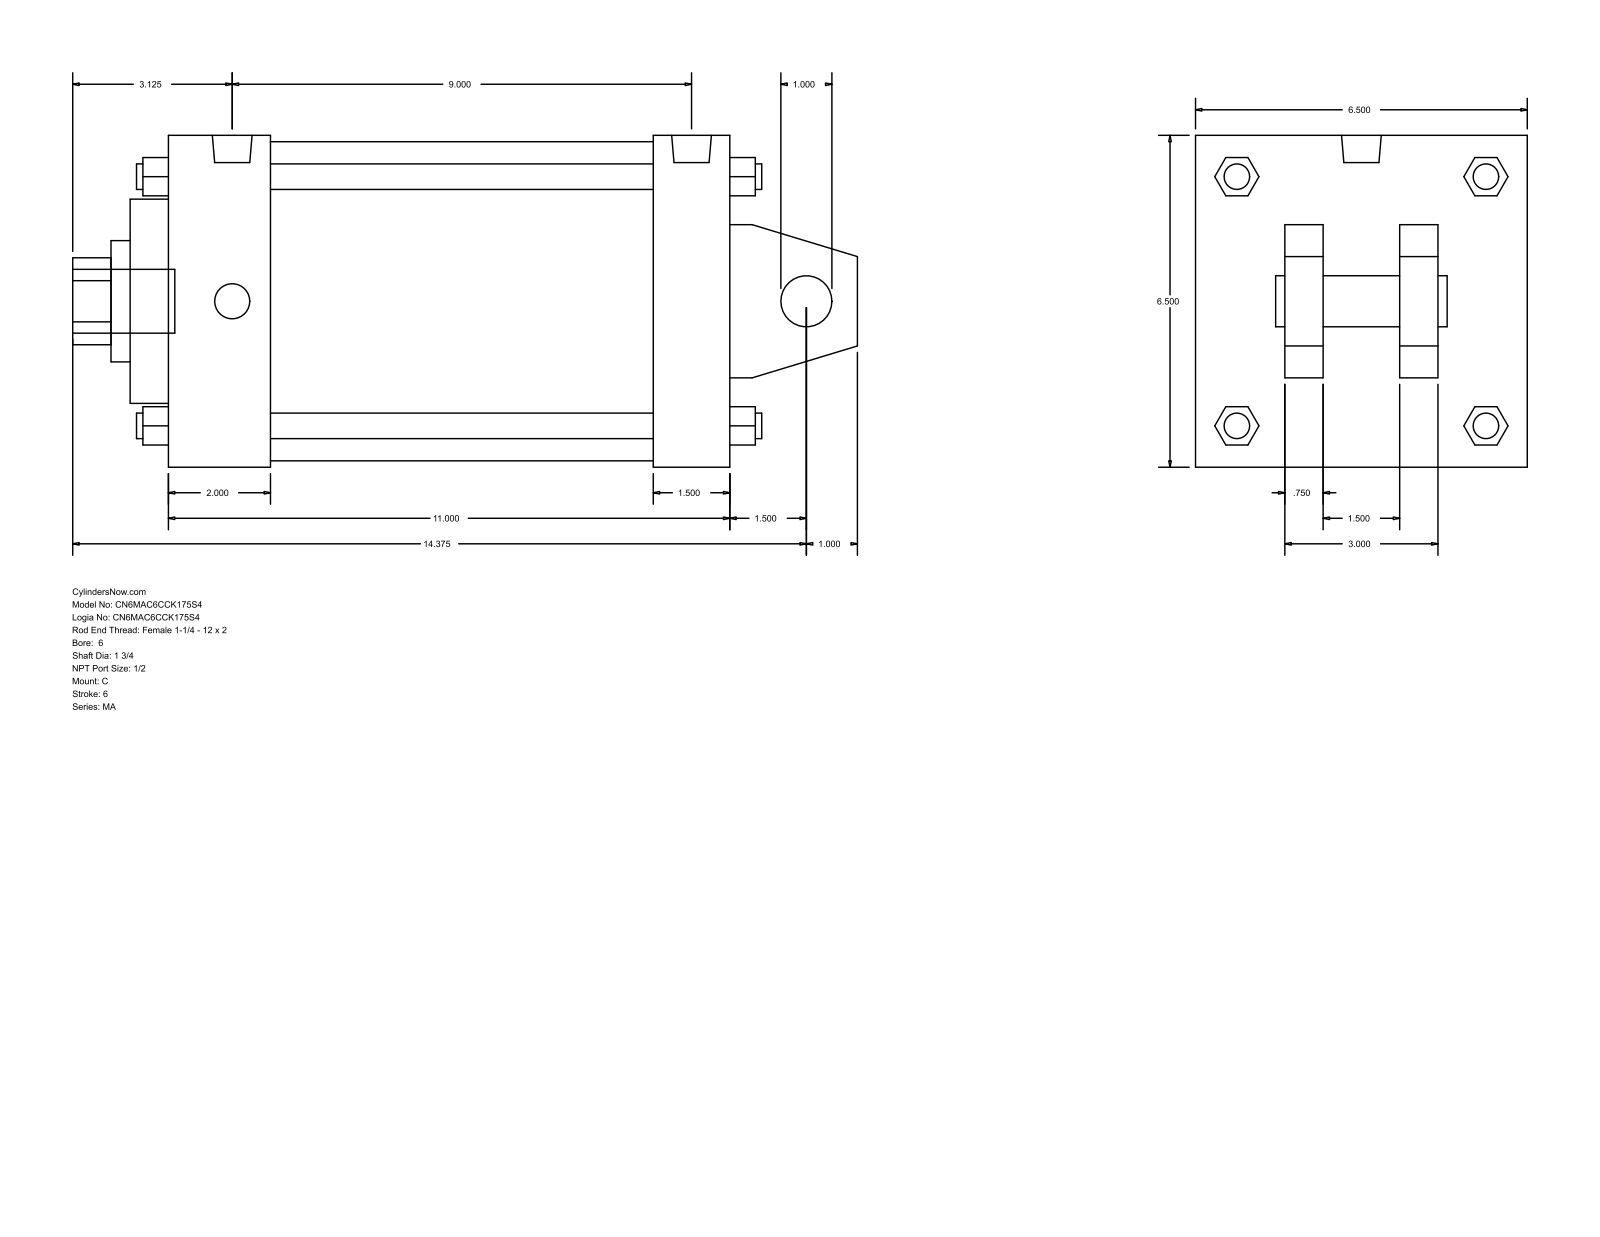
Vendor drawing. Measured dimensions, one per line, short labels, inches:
name: MA_C__0600_1.75
written by: GSSL Pune (CONFIG_CONTROL_DESIGN)
unit: in
bodies: 0 solids, 141 faces (109 planar, 32 cylindrical, 0 other)
size: 15.375 × 6.5 × 6.5
holes: 1× ⌀1, 1× ⌀1.75, 1× ⌀2.375, 1× ⌀4, 1× ⌀6.25
bosses: 4× ⌀0.687, 4× ⌀0.5, 2× ⌀0.778, 1× ⌀1.25
rounds: 1× R0.852
face distances: 6.5, 11, 0.75, 2.5, 4, 2, 4.75, 1.75, 9.5, 2.25
